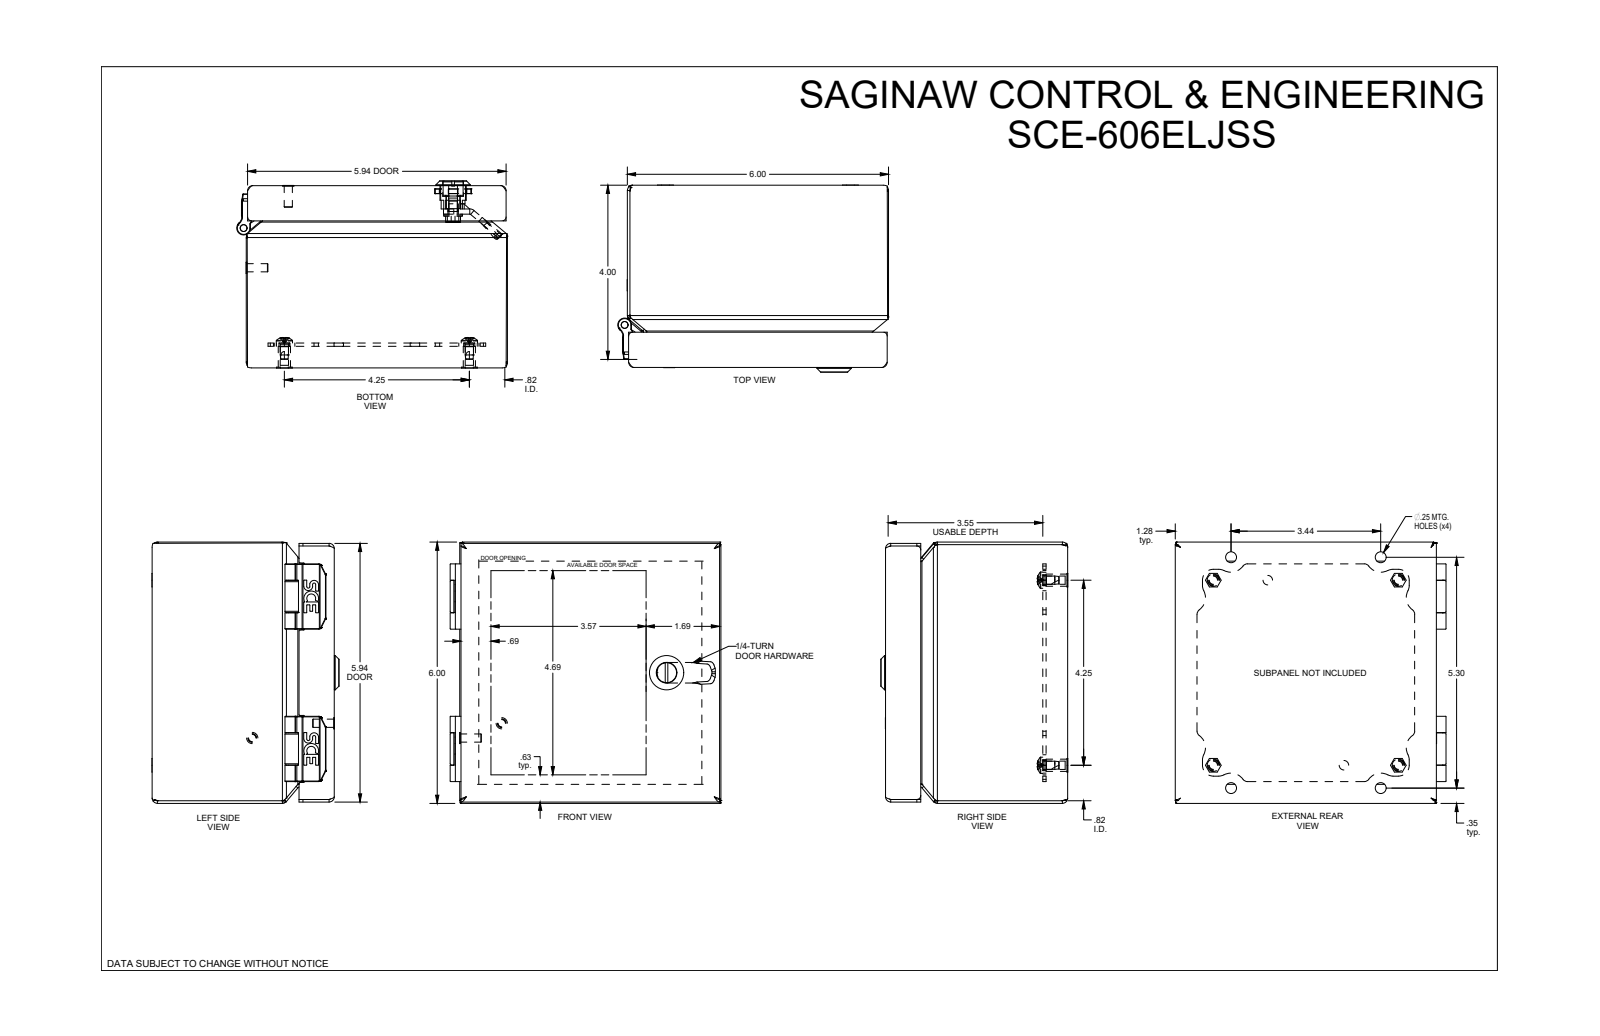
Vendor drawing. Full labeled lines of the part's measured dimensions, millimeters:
Part name (STEP PRODUCT): SCE-606ELJSS
STEP written by: SolidWorks 2019 (CONFIG_CONTROL_DESIGN)
Units: millimetres
Bodies: 0 solids, 2717 faces (863 planar, 790 cylindrical, 1064 other)
Overall size (bounding box): 158 × 152.4 × 109.1
Round holes (diameter × count): ⌀6.4 ×8, ⌀4.8 ×4, ⌀7.2 ×4, ⌀12.2 ×4, ⌀0.5 ×2, ⌀2.5 ×2, ⌀4.4 ×2, ⌀5 ×2, ⌀5.5 ×2, ⌀6.8 ×2, ⌀4 ×1, ⌀5.1 ×1
Round bosses / shafts (diameter × count): ⌀4.8 ×6, ⌀9.5 ×4, ⌀7.1 ×4, ⌀4.3 ×4, ⌀4.1 ×4, ⌀3.4 ×4, ⌀2.7 ×4, ⌀6.6 ×2
Partial cylindrical surfaces — rounded edges, fillets, slot ends (radius × count): R2.7 ×132, R0.1 ×131, R0.2 ×32, R0.2 ×26, R0.6 ×24, R0.8 ×24, R3 ×23, R1.5 ×22
Main face-to-face distances: 1.5, 150.9, 1.5, 149.4, 152.4, 104.7, 103.3, 106.3, 104.8, 14.5
Hole centre spacings: 16.9, 98.6, 108, 121.7, 155.7, 25.2, 31.8, 54.8
